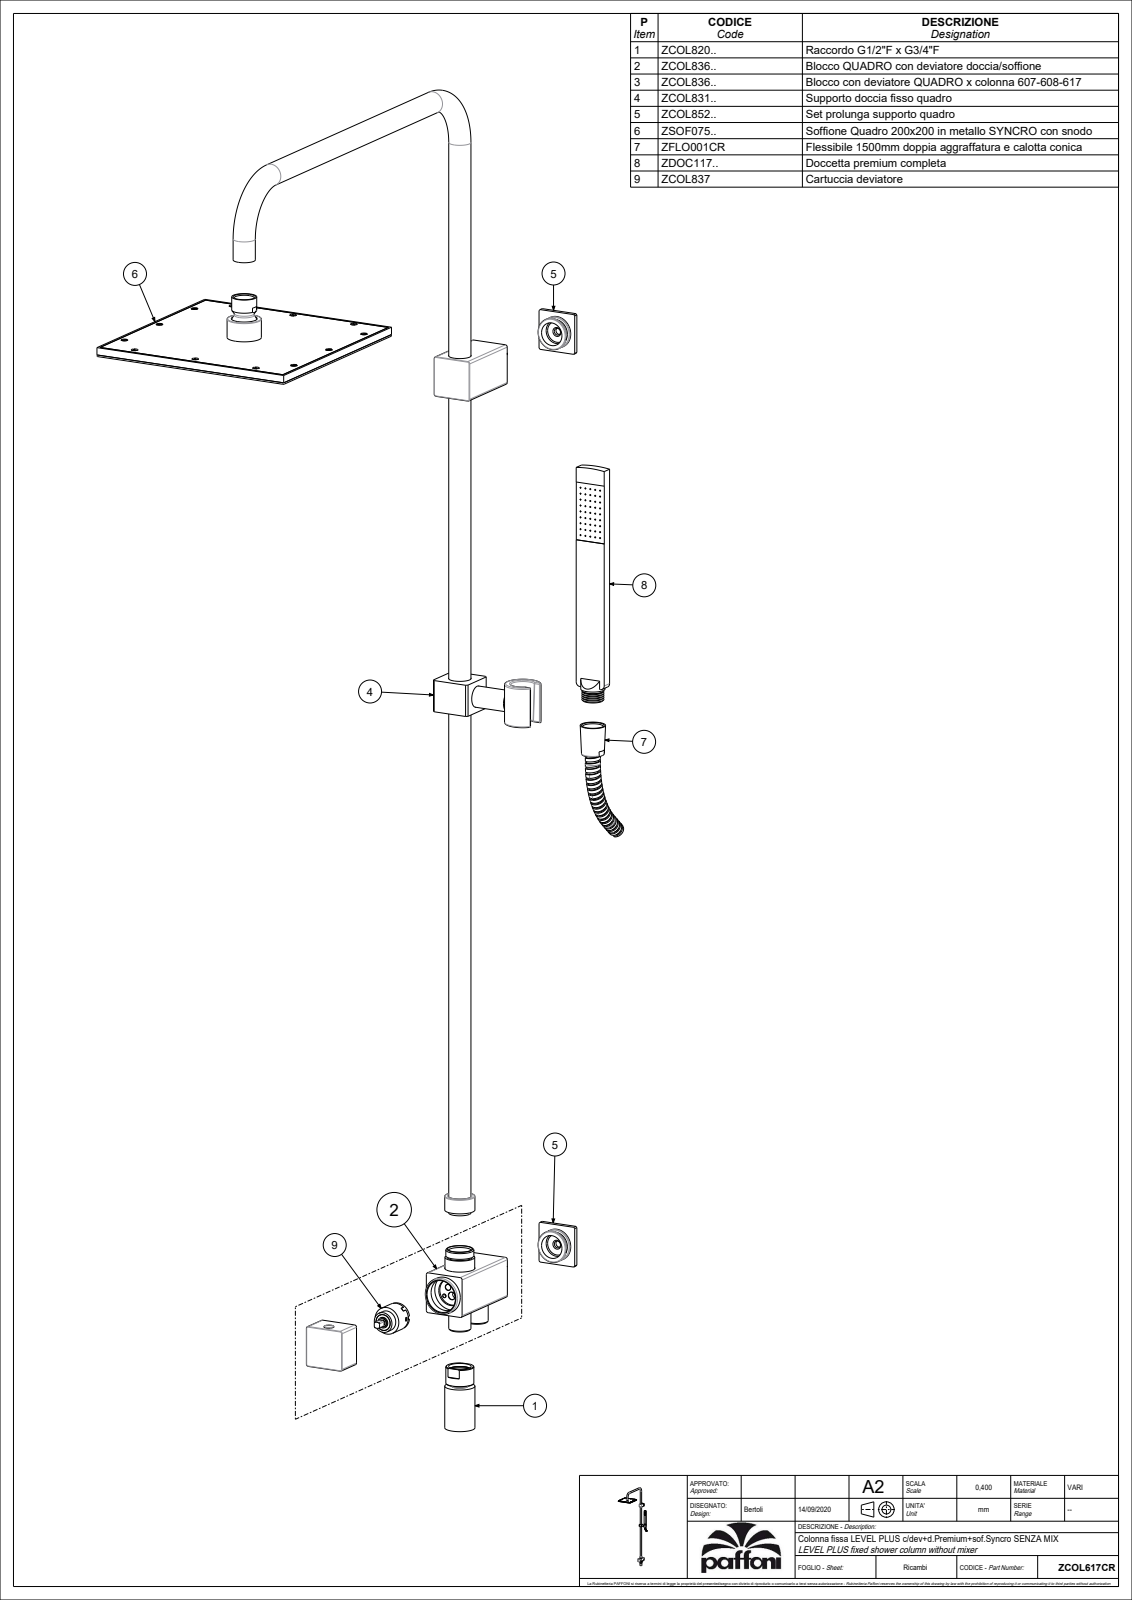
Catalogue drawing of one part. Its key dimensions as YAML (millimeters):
part_name: "ZCOL617CR"
step_written_by: "CREO PARAMETRIC BY PTC INC, 2020044 (CONFIG_CONTROL_DESIGN)"
units: millimeters
bodies: {solids: 5, faces: 6151, planar: 1107, cylindrical: 1242, other: 3802}
overall_size: [1205.3, 559.1, 200.2]
volume: 623612
surface_area: 493655
round_holes:
  - {diameter: 1.5, count: 100}
  - {diameter: 1.7, count: 100}
  - {diameter: 6, count: 14}
  - {diameter: 7, count: 14}
  - {diameter: 2.5, count: 12}
  - {diameter: 5.1, count: 12}
  - {diameter: 5.5, count: 3}
  - {diameter: 15, count: 3}
  - {diameter: 19, count: 3}
  - {diameter: 4.2, count: 2}
  - {diameter: 6.5, count: 2}
  - {diameter: 8, count: 2}
round_bosses_or_shafts:
  - {diameter: 10, count: 101}
  - {diameter: 5, count: 15}
  - {diameter: 2, count: 11}
  - {diameter: 20.6, count: 4}
  - {diameter: 29.7, count: 2}
  - {diameter: 24.8, count: 2}
  - {diameter: 12.8, count: 2}
  - {diameter: 34.4, count: 1}
partial_cylinders:
  - {radius: 0.3, count: 48}
  - {radius: 0.5, count: 22}
  - {radius: 1, count: 16}
  - {radius: 0.2, count: 12}
  - {radius: 20, count: 12}
  - {radius: 2, count: 10}
  - {radius: 0.43, count: 6}
  - {radius: 1.5, count: 4}
face_to_face_distances: [8.5, 1, 7.5, 1.5, 7, 6, 2.9, 1.4, 4.6, 5.6]
hole_center_spacings: [16.3, 36.45, 23.05, 51.55, 32.6, 67.21, 48.9, 83.11]
